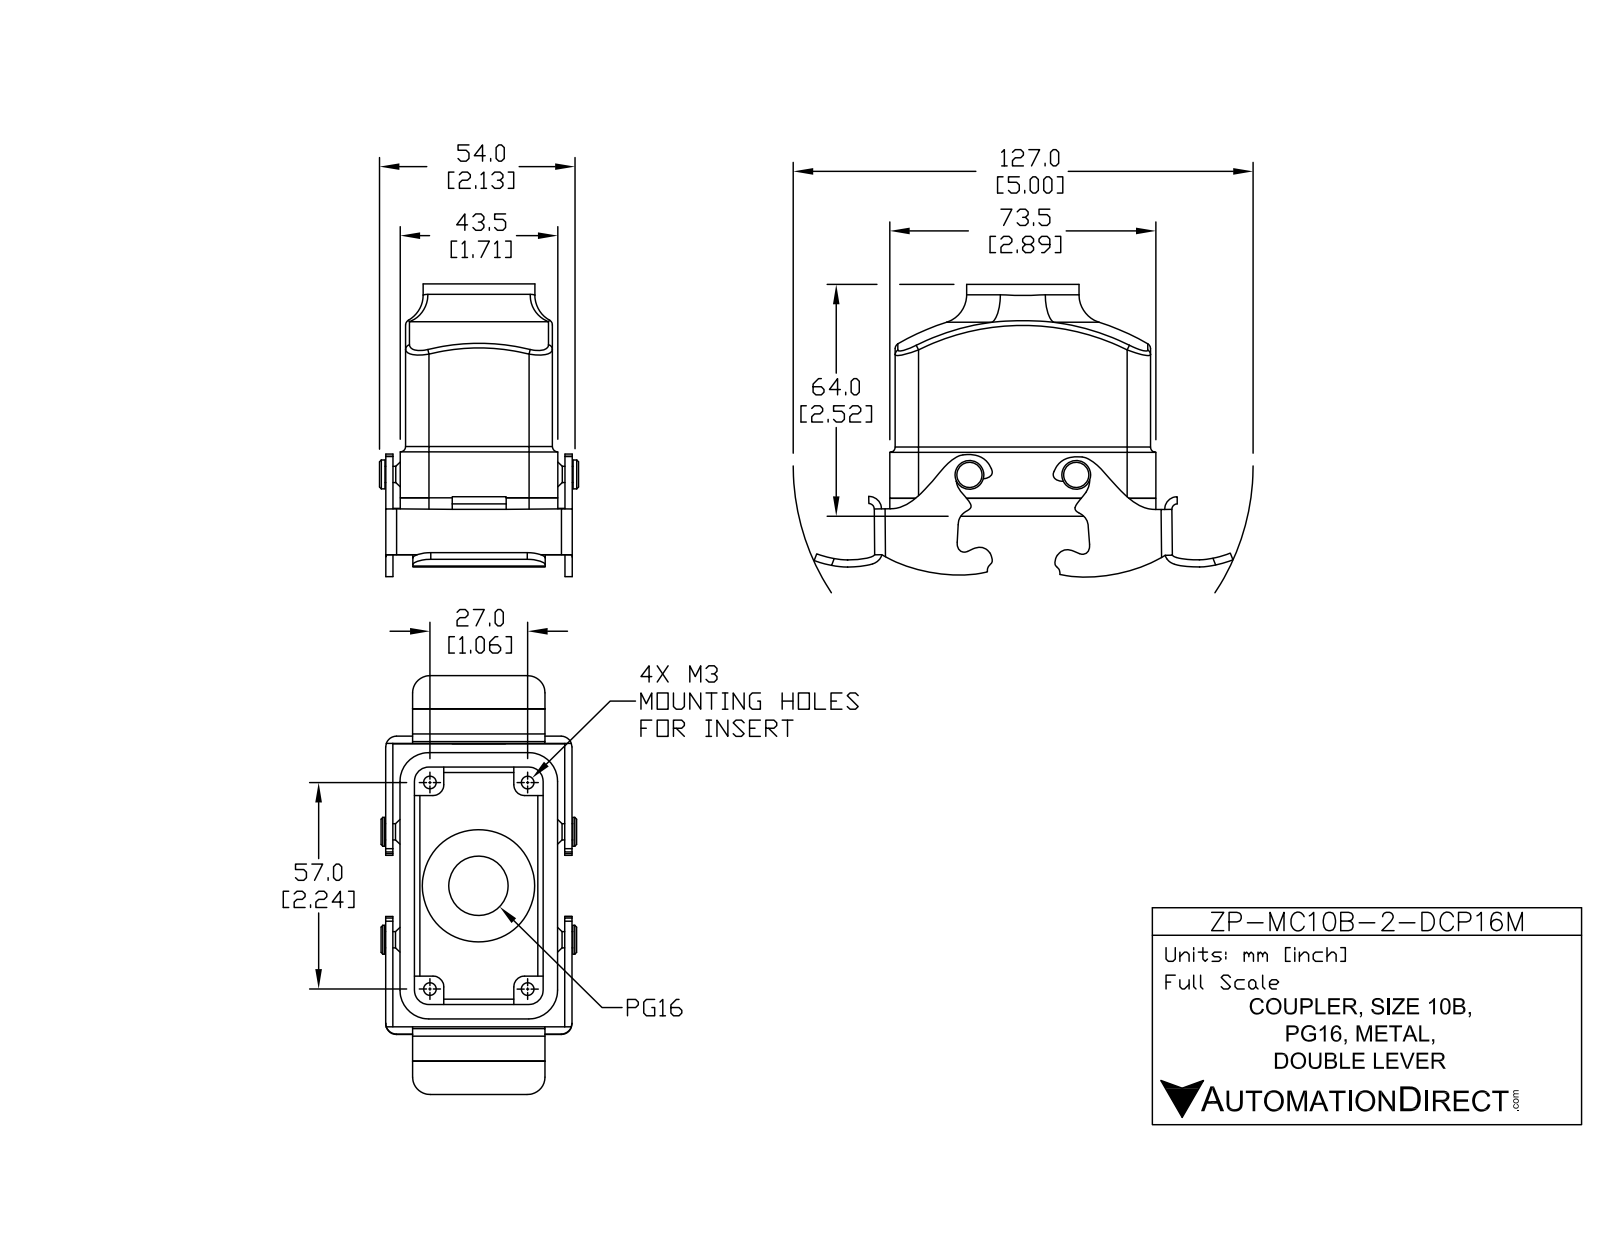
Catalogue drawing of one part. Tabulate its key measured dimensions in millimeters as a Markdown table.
| quantity | value |
| --- | --- |
| part name | ZP-MC10B-2-DCP16M |
| STEP written by | SolidWorks 2011 (AUTOMOTIVE_DESIGN) |
| units | millimeters |
| bodies | 4 solids, 306 faces (122 planar, 145 cylindrical, 39 other) |
| overall size | 106.59 × 77.52 × 55.5 |
| volume | 66 637 mm³ |
| surface area | 43 823 mm² |
| round holes (diameter × count) | 3.5 × 4, 16.5 × 1, 21 × 1 |
| round bosses / shafts (diameter × count) | 8 × 2, 4.52 × 2, 31.25 × 1 |
| partial cylindrical surfaces (radius × count) | 0.5 × 18, 3 × 10, 2 × 6, 4 × 6, 1 × 4, 1.5 × 4, 5.5 × 4, 6.5 × 4 |
| main face-to-face distances | 4, 1.5, 1, 38.5, 37, 5.5, 6.75, 2.5, 2.75, 39.75 |
| hole center spacings | 30.88, 25.66, 56.18, 61.76 |
